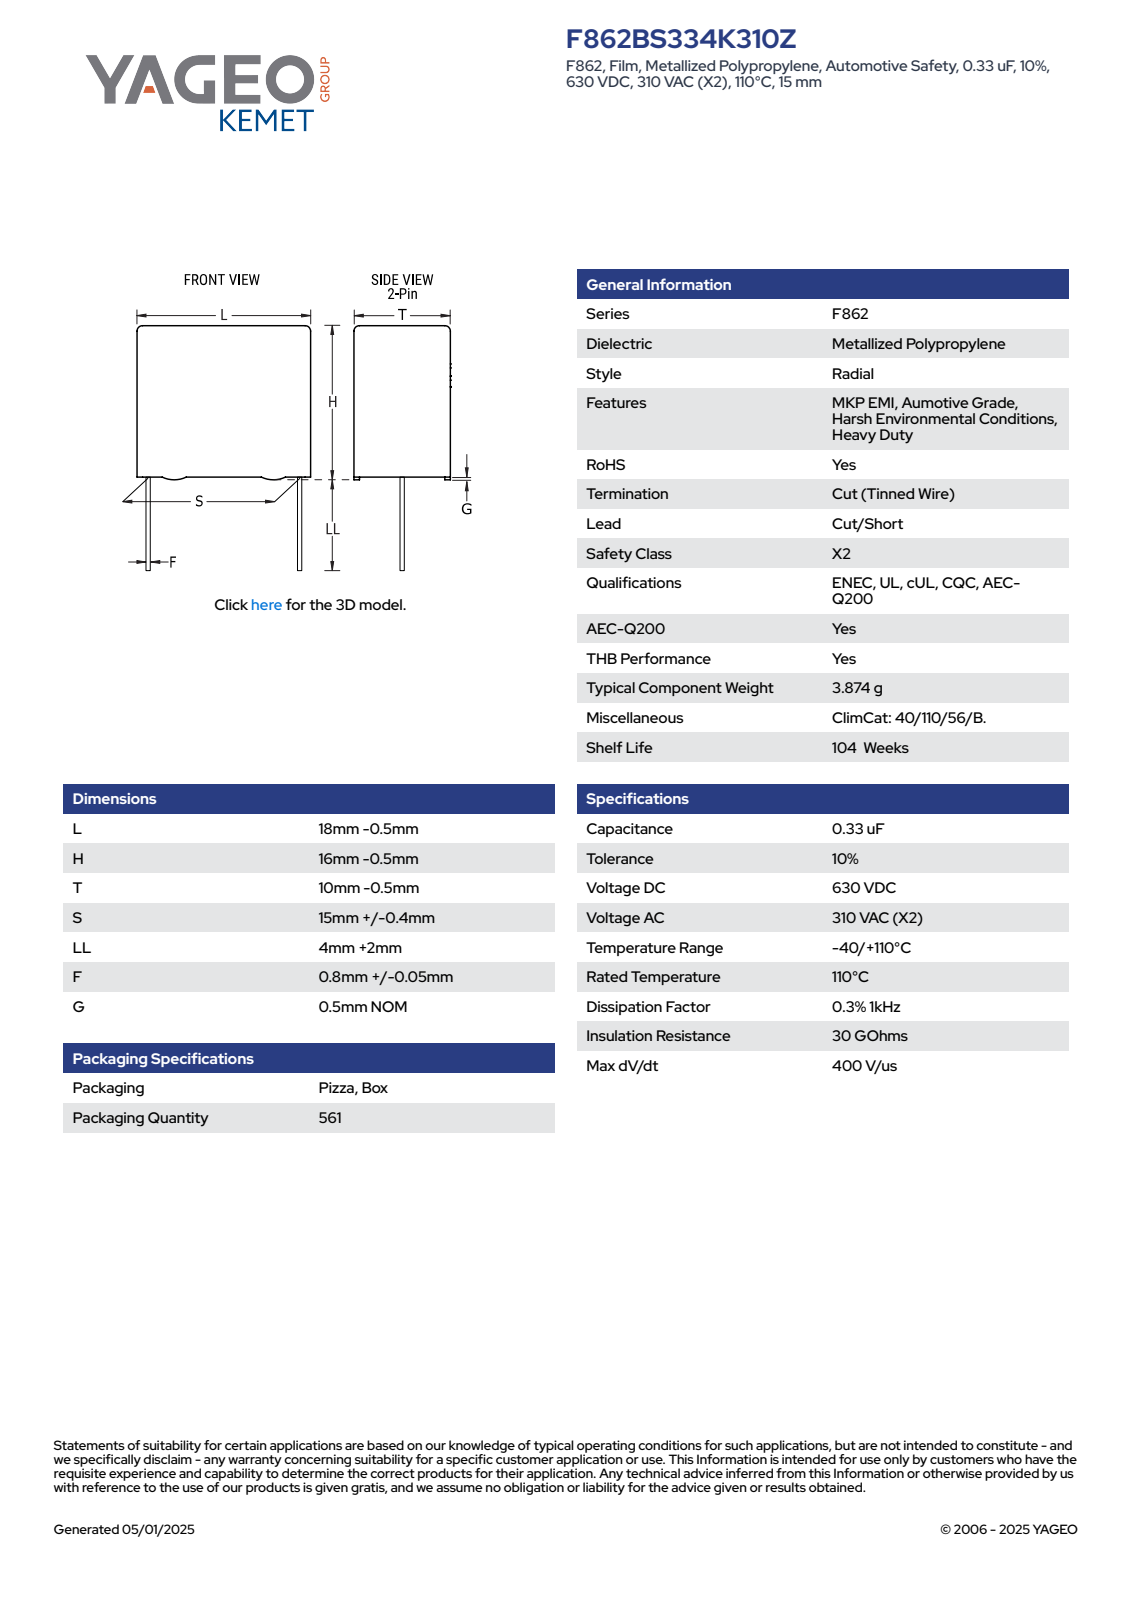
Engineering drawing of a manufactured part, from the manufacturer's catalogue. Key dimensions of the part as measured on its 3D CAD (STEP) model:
Part name (STEP PRODUCT): CFR_RBG_18X16X10_L17.5H15.5T9.5S15LL6F0.85G0.5
STEP written by: SolidWorks 2014 (AUTOMOTIVE_DESIGN)
Units: millimetres
Bodies: 4 solids, 89 faces (81 planar, 8 cylindrical, 0 other)
Overall size (bounding box): 21.5 × 17.5 × 9.51
Volume: 2 501 mm³ · Surface area: 1 212 mm²
Round bosses / shafts (diameter × count): ⌀0.85 ×2
Partial cylindrical surfaces — rounded edges, fillets, slot ends (radius × count): R0.5 ×4
Main face-to-face distances: 9.5, 15, 17.5, 0.5, 15.5, 0.54, 8.96, 8.42, 6, 6.5
